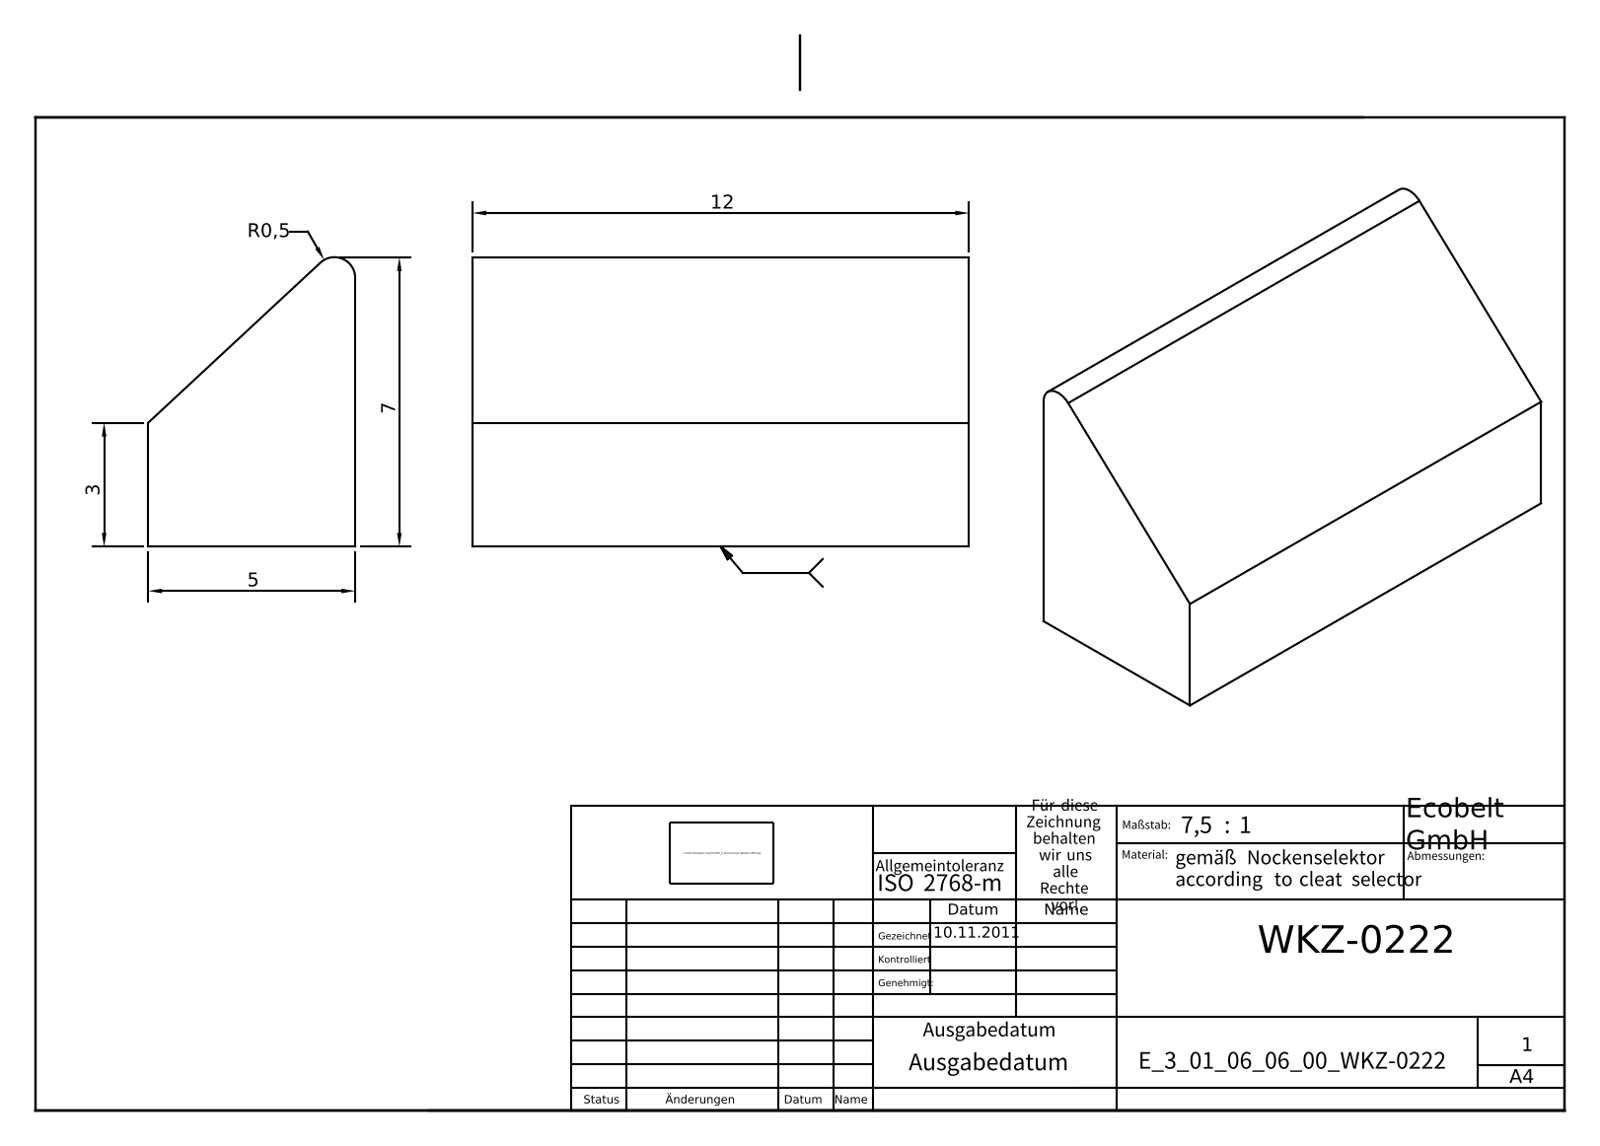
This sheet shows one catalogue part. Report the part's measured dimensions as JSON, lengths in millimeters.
{"part_name": "E_3_01_06_06_00_WKZ-0222", "step_written_by": "Autodesk Inventor 2025 (AUTOMOTIVE_DESIGN)", "units": "millimeters", "bodies": {"solids": 1, "faces": 7, "planar": 6, "cylindrical": 1, "other": 0}, "overall_size": [12, 7, 5], "volume_mm3": 316, "surface_area_mm2": 309, "partial_cylinders_radius": [[0.5, 1]], "face_to_face_distances": [5, 12]}
